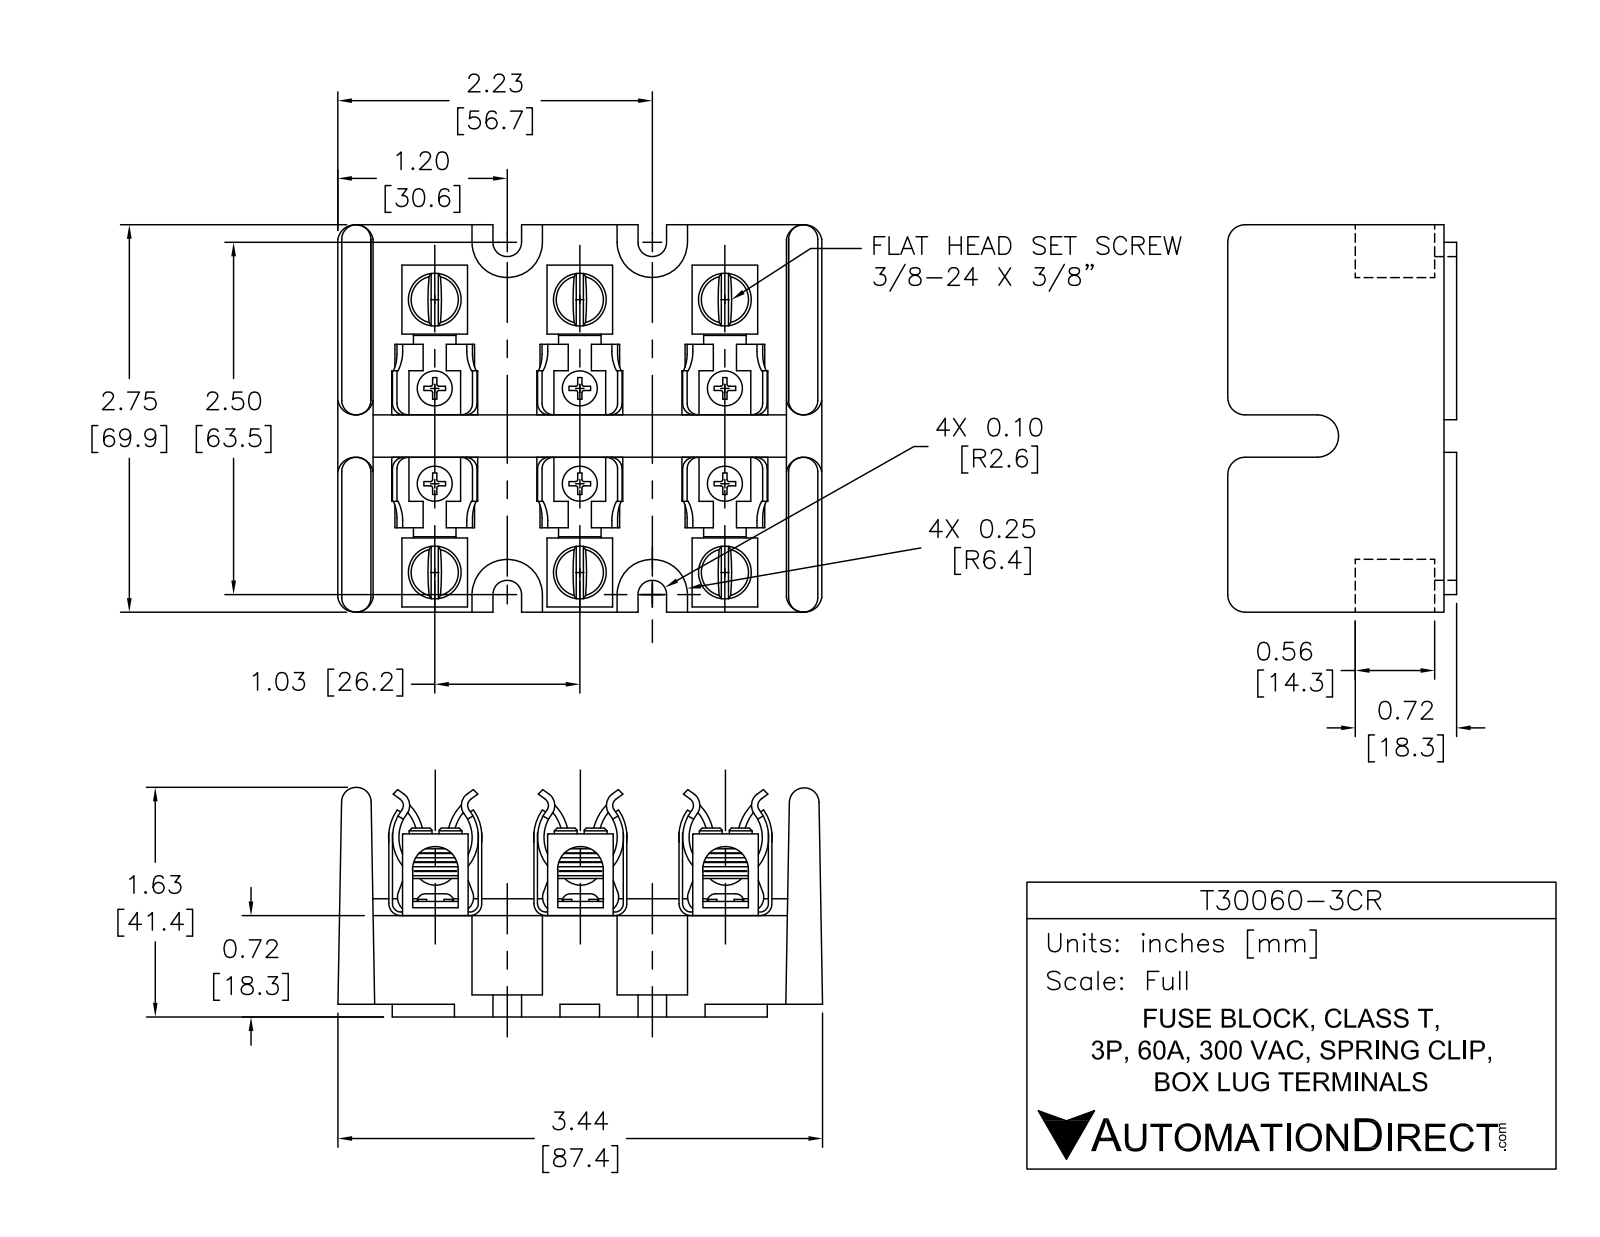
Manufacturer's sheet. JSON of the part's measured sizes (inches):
{"part_name": "T30060-3CR", "step_written_by": "SolidWorks 2019 (AUTOMOTIVE_DESIGN)", "units": "inches", "bodies": {"solids": 13, "faces": 520, "planar": 248, "cylindrical": 236, "other": 36}, "overall_size": [3.441, 2.75, 1.63], "volume_in3": 8.268, "surface_area_in2": 71.39, "round_holes": [[0.319, 6]], "round_bosses_or_shafts": [[0.315, 6]], "partial_cylinders_radius": [[0.2, 24], [0.24, 12], [0.125, 10], [0.25, 7], [0.16, 6], [0.2, 6], [0.1, 4], [0.375, 4]], "face_to_face_distances": [0.68, 0.74, 0.06, 3.441, 0.25, 3.191, 1.03, 2.75, 2.941, 0.78], "hole_center_spacings": [1.03, 2.258, 2.01, 2.06, 2.878]}
